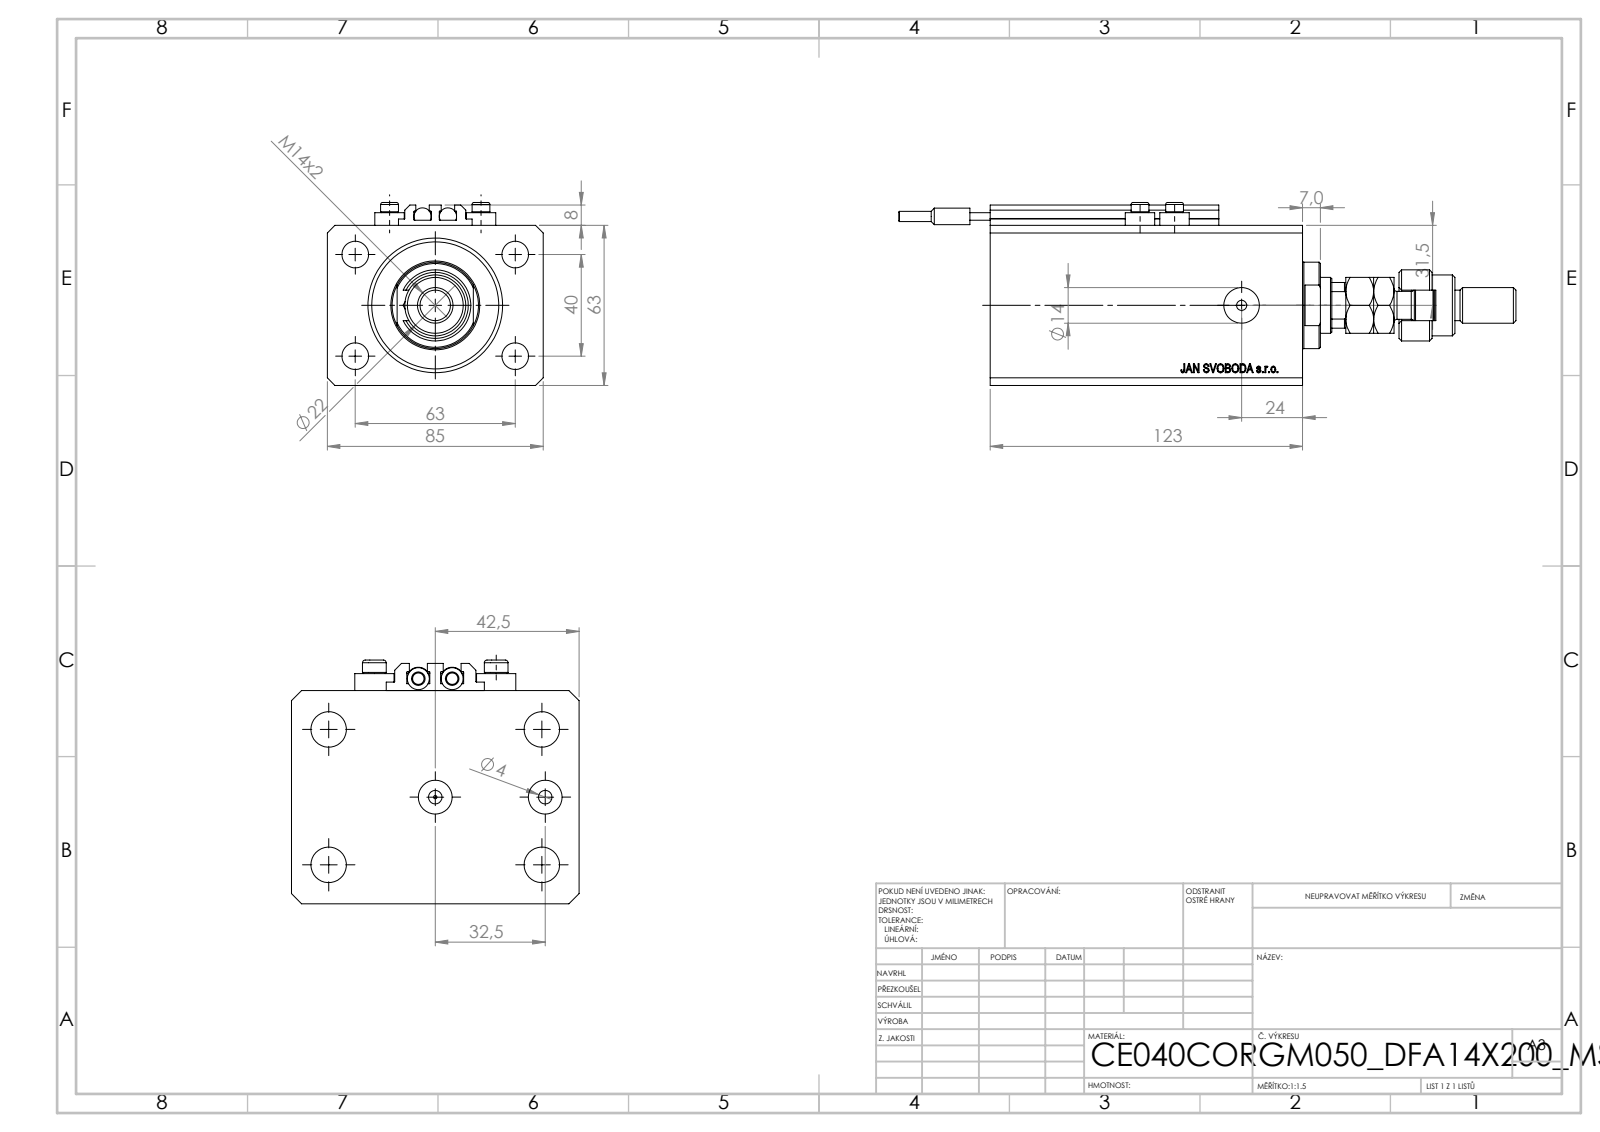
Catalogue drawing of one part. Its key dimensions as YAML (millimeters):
part_name: "MFA; V250CE_VC_C; SWITCH_V250CE; V250CE_C_Body (+3 more)"
step_written_by: "SolidWorks 2019 (CONFIG_CONTROL_DESIGN)"
units: millimeters
bodies: {solids: 12, faces: 1175, planar: 564, cylindrical: 113, other: 498}
overall_size: [243, 85, 72]
volume: 612345
surface_area: 124896
round_holes:
  - {diameter: 4, count: 8}
  - {diameter: 10.5, count: 4}
  - {diameter: 10, count: 2}
  - {diameter: 14, count: 2}
  - {diameter: 1.25, count: 1}
  - {diameter: 12.5, count: 1}
  - {diameter: 22, count: 1}
  - {diameter: 40, count: 1}
  - {diameter: 53, count: 1}
round_bosses_or_shafts:
  - {diameter: 11.6, count: 4}
  - {diameter: 7, count: 4}
  - {diameter: 6.8, count: 2}
  - {diameter: 6.5, count: 2}
  - {diameter: 4, count: 2}
  - {diameter: 34, count: 1}
  - {diameter: 28, count: 1}
  - {diameter: 24, count: 1}
partial_cylinders:
  - {radius: 0.2, count: 10}
  - {radius: 9.75, count: 1}
  - {radius: 10.5, count: 1}
face_to_face_distances: [63, 85, 123, 17, 106, 11.4, 94.6, 111.6, 3, 2]
hole_center_spacings: [37.31, 13.6, 20.02, 36, 38.48, 40, 63, 67.05]
